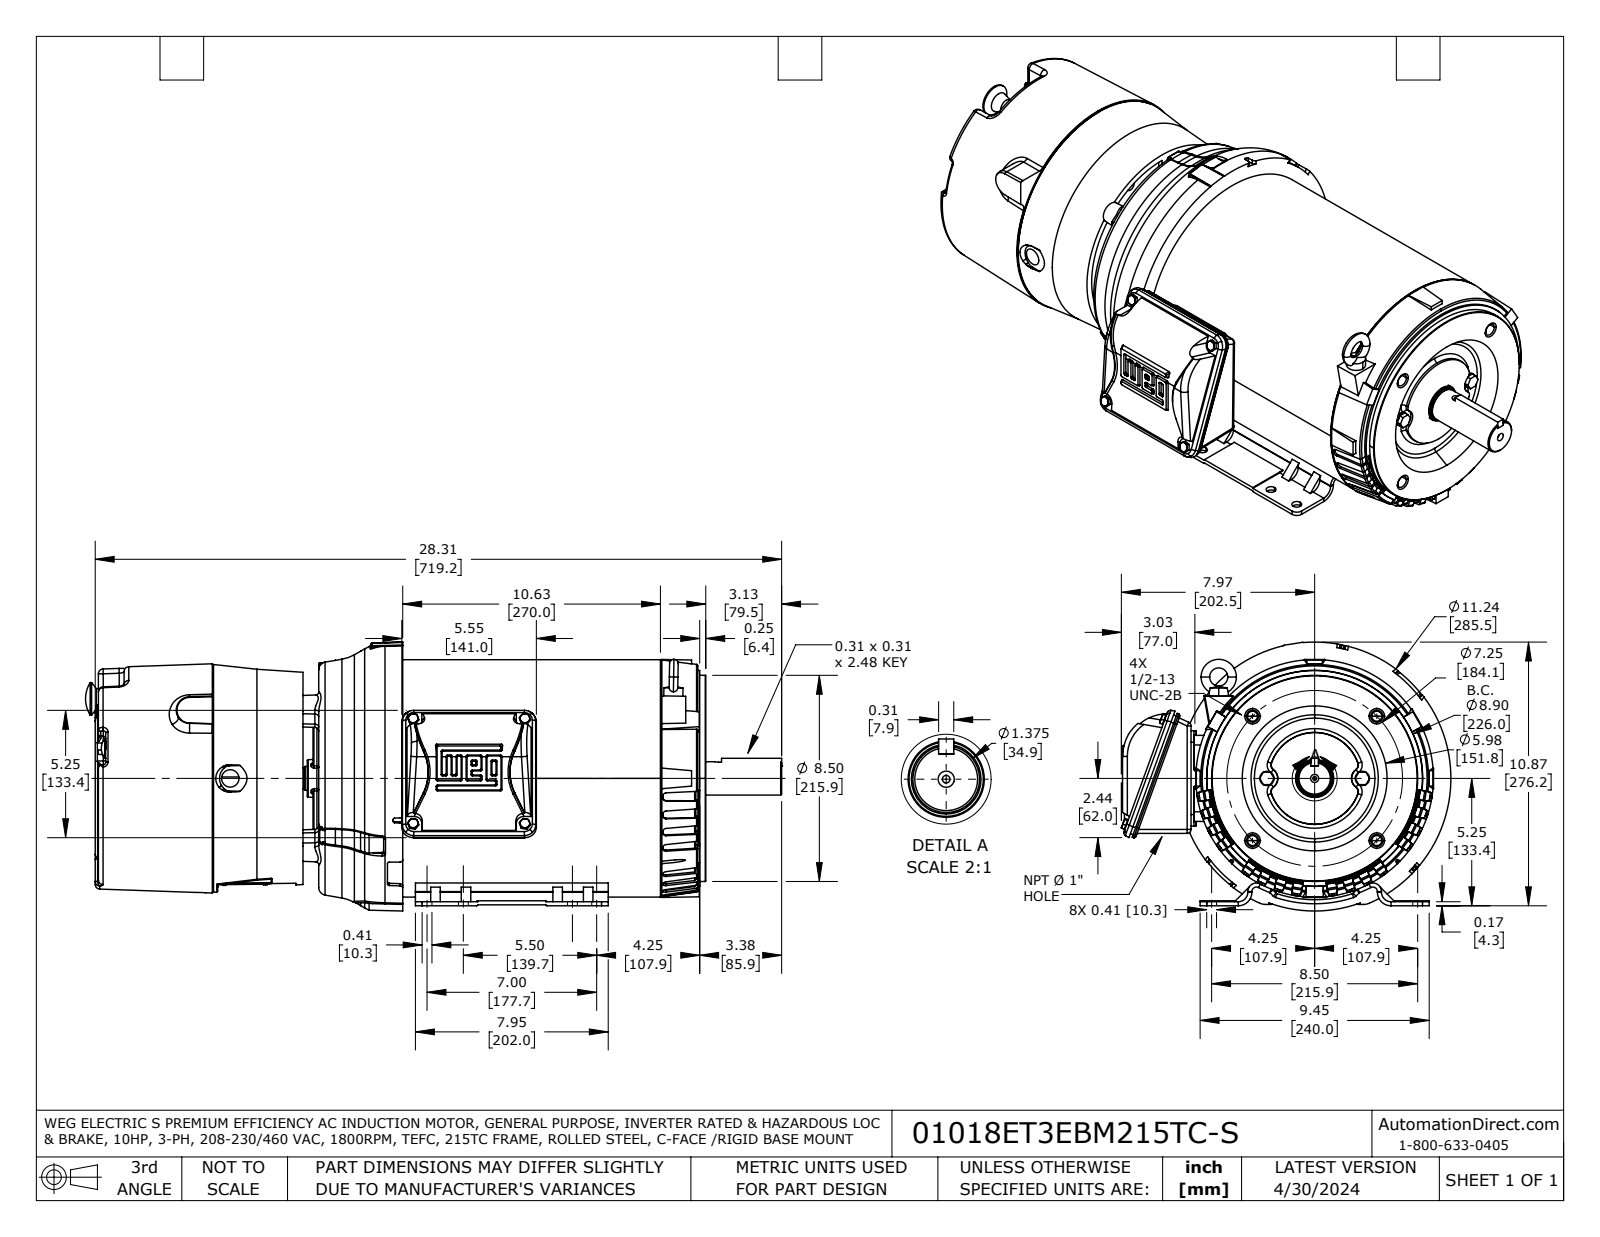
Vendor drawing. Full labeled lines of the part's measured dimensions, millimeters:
Part name (STEP PRODUCT): 001018ET3EBM215TC-S
STEP written by: SolidWorks 2021 (AUTOMOTIVE_DESIGN)
Units: millimetres
Bodies: 29 solids, 3384 faces (1166 planar, 678 cylindrical, 1540 other)
Overall size (bounding box): 729.2 × 345.3 × 281.6
Volume: 25 100 000 mm³ · Surface area: 1 564 000 mm²
Round holes (diameter × count): ⌀10.3 ×8, ⌀6.5 ×6, ⌀12.7 ×5, ⌀2.6 ×4, ⌀3.7 ×4, ⌀10.5 ×4, ⌀10.7 ×4, ⌀5.1 ×3, ⌀13.5 ×3, ⌀14.4 ×3, ⌀21.4 ×3, ⌀26.2 ×3
Round bosses / shafts (diameter × count): ⌀9 ×4, ⌀2.8 ×4, ⌀20.6 ×3, ⌀12.7 ×3, ⌀15 ×2, ⌀11.6 ×2, ⌀248.6 ×1, ⌀238.3 ×1
Partial cylindrical surfaces — rounded edges, fillets, slot ends (radius × count): R1.5 ×58, R3.2 ×32, R2.5 ×29, R2 ×24, R3 ×24, R1.3 ×23, R5.1 ×22, R1 ×19
Main face-to-face distances: 270, 81.4, 351.4, 232.7, 314, 584, 4.8, 8.1, 240.8, 322.2
Hole centre spacings: 101.6, 38.1, 46.2, 56.2, 66.8, 92.1, 101.5, 130.2
